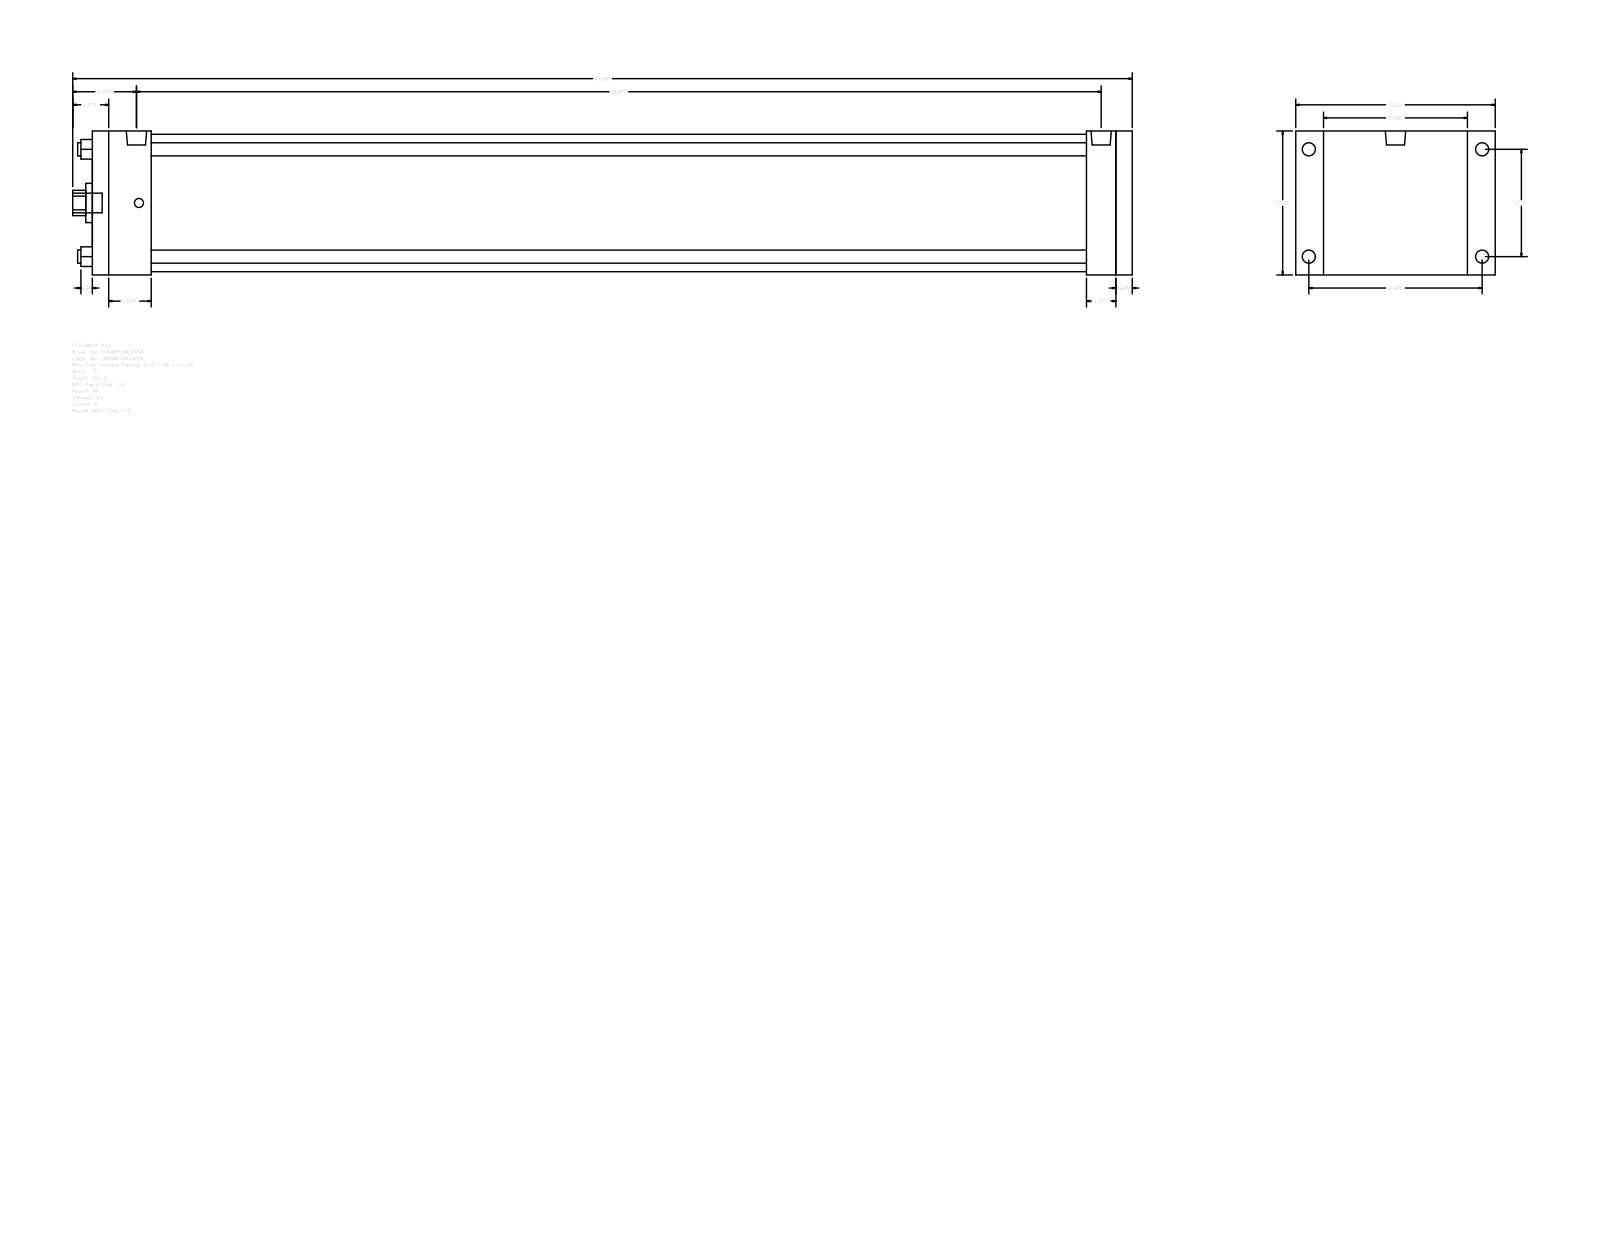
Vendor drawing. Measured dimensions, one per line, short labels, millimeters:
name: A_RF__0500_1
written by: GSSL Pune (CONFIG_CONTROL_DESIGN)
unit: mm
bodies: 0 solids, 92 faces (64 planar, 28 cylindrical, 0 other)
size: 1028.7 × 193.68 × 139.7
holes: 4× ⌀12.7, 1× ⌀25.4, 1× ⌀38.1, 1× ⌀133.35
bosses: 4× ⌀12.7, 4× ⌀8.73, 2× ⌀19.77, 1× ⌀19.05
rounds: 1× R12.29
face distances: 139.7, 1009.65, 15.87, 993.78, 57.15, 936.63, 952.5, 965.2, 908.05, 28.58
hole spacings: 73.64, 104.14, 147.28
